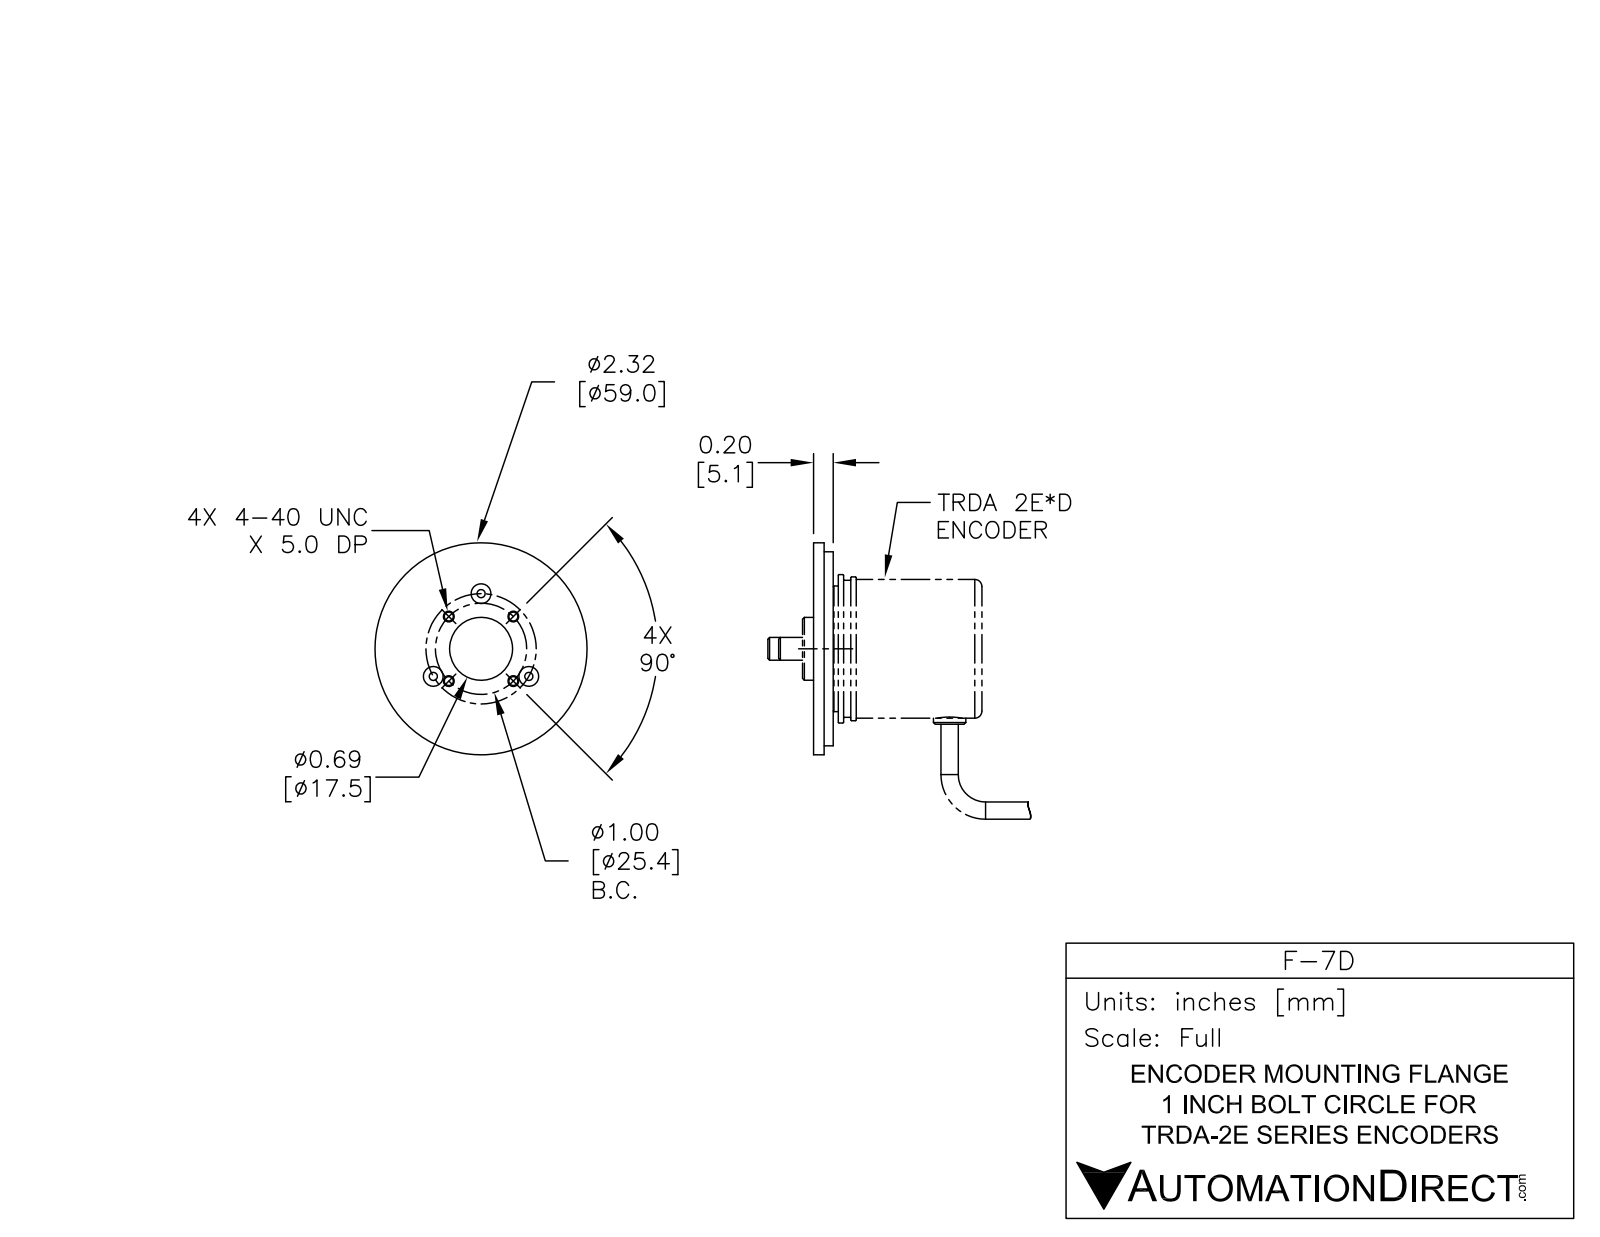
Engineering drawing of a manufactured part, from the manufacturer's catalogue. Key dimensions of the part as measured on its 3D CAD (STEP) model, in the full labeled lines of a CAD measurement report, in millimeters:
Part name (STEP PRODUCT): F-7D
STEP written by: SolidWorks 2017 (AUTOMOTIVE_DESIGN)
Units: millimetres
Bodies: 5 solids, 62 faces (16 planar, 38 cylindrical, 8 other)
Overall size (bounding box): 59 × 59 × 8.1
Volume: 12 100 mm³ · Surface area: 7 323 mm²
Round holes (diameter × count): ⌀2.3 ×4, ⌀3 ×3, ⌀5 ×3, ⌀10 ×1, ⌀19.1 ×1
Round bosses / shafts (diameter × count): ⌀2.8 ×4, ⌀59 ×1, ⌀54 ×1, ⌀17.4 ×1
Main face-to-face distances: 5.1, 2.5, 2.5, 2.6, 8.1, 5.6, 5.6, 3, 2.1, 0.4
Hole centre spacings: 12.7, 18, 26.6, 4.5, 11, 15.3, 17.2, 22.3
